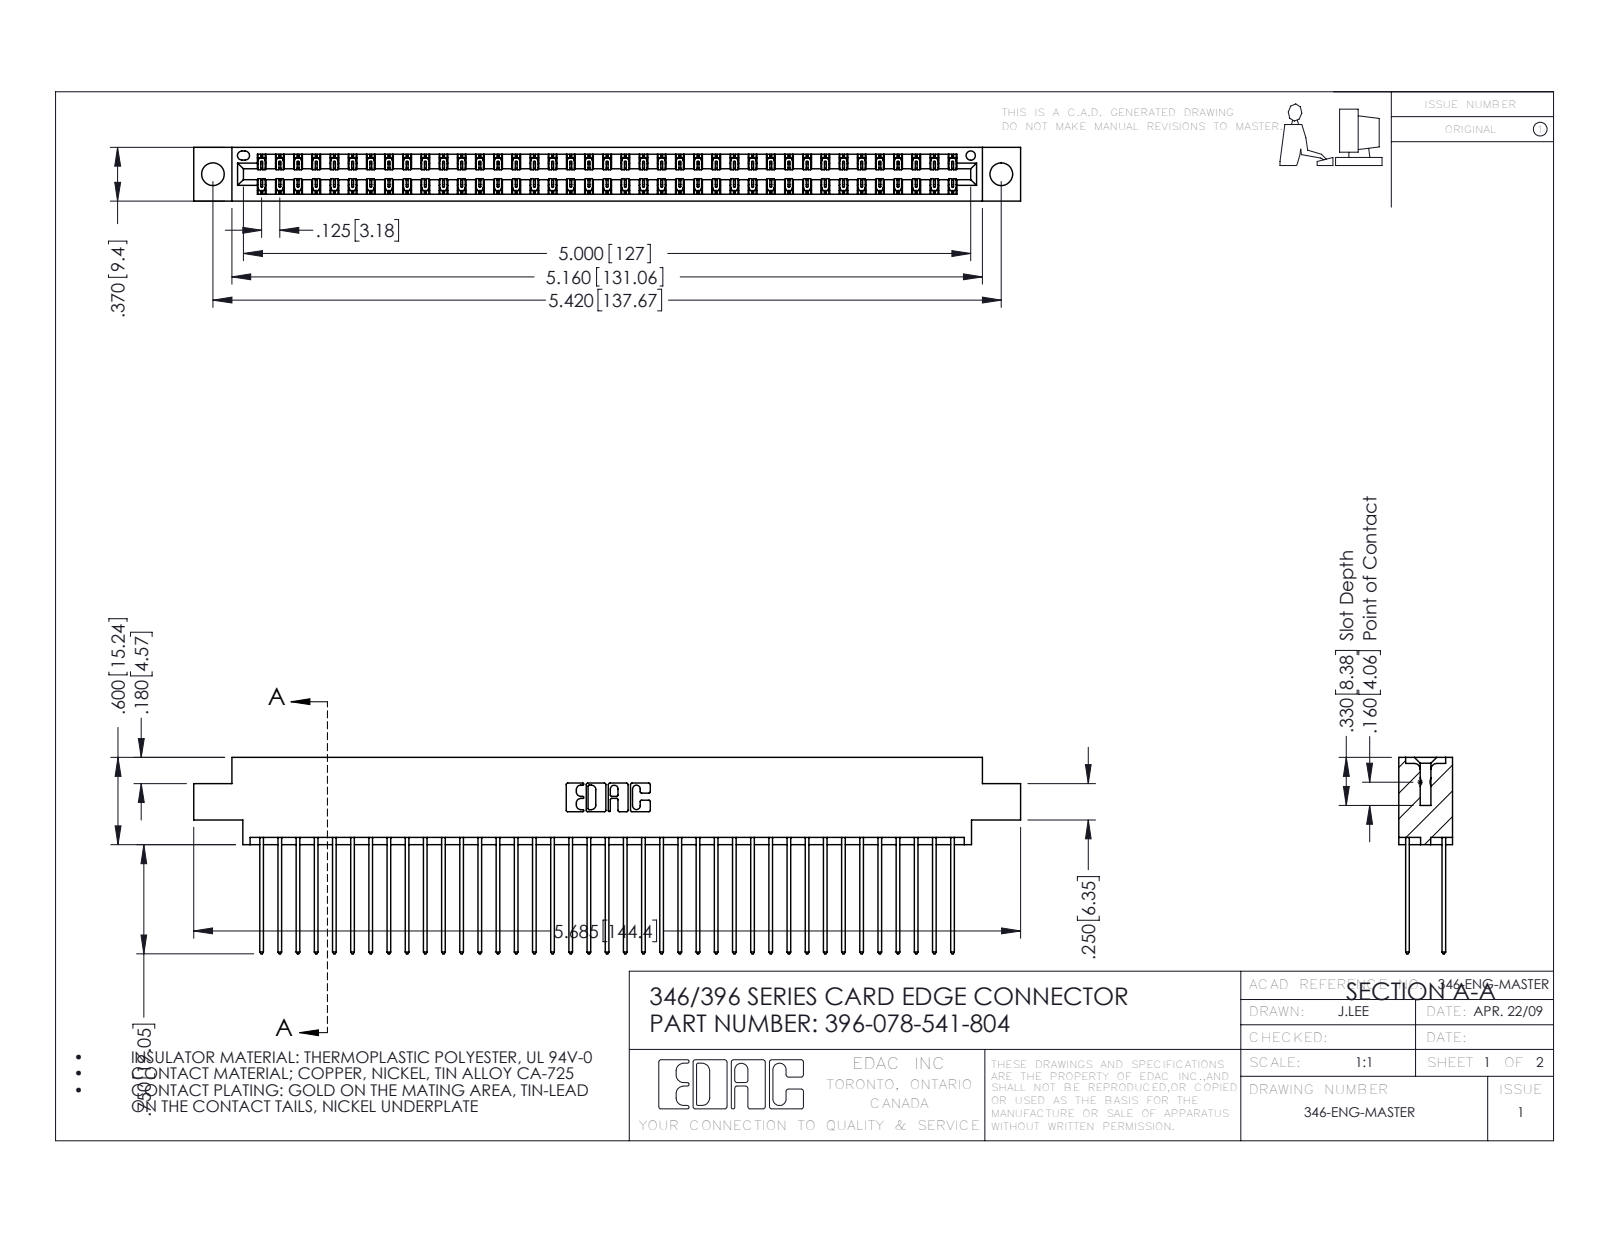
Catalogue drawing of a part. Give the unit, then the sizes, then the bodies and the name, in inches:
Units: inches
Overall size (bounding box): 5.685 × 1.35 × 0.37
Round holes (diameter × count): ⌀0.156 ×2, ⌀0.064 ×1
Partial cylindrical surfaces — rounded edges, fillets, slot ends (radius × count): R0.006 ×117, R0.01 ×78, R0.01 ×22, R0.007 ×6, R0.031 ×6, R0.026 ×3, R0.014 ×2, R0.022 ×2
Main face-to-face distances: 0.048, 0.322, 0.25, 0.072, 0.298, 0.025, 0.37, 0.275, 0.225, 0.148
Hole centre spacings: 0.246, 5.211, 5.42
Volume: 0.87 in³ · Surface area: 33.63 in²
Bodies: 79 solids, 4182 faces (2810 planar, 1372 cylindrical, 0 other)
Part name (STEP PRODUCT): 396-078-541-804; 346 Part_0.170 Offset - 0.156 Dia-TH; 345-292-001_345-293-141
STEP written by: SolidWorks 2016 (CONFIG_CONTROL_DESIGN)
